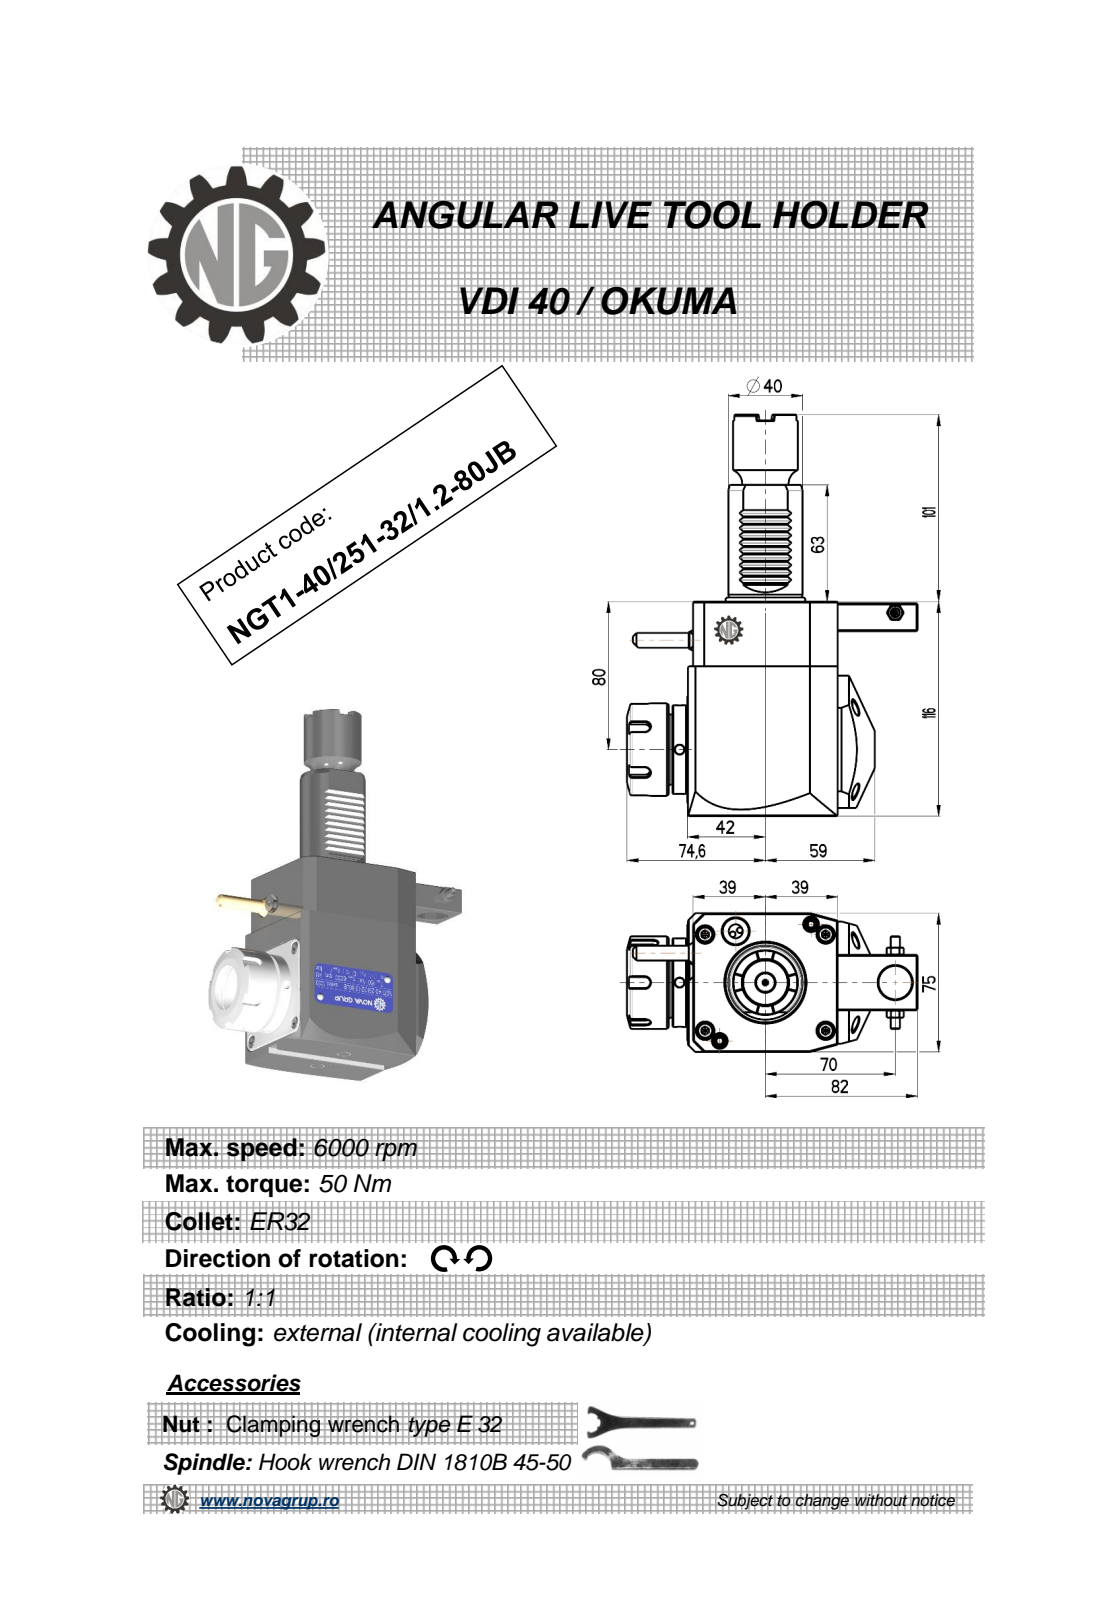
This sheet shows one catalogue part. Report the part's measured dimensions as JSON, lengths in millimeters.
{"part_name": "NGT1_40_251_32_1_2_80JB", "step_written_by": "PRO/ENGINEER BY PARAMETRIC TECHNOLOGY CORPORATION, 2010280 (CONFIG_CONTROL_DESIGN)", "units": "millimeters", "bodies": {"solids": 1, "faces": 466, "planar": 209, "cylindrical": 92, "other": 165}, "overall_size": [217, 156.6, 76.6], "volume_mm3": 914770, "surface_area_mm2": 76313, "round_holes": [[5, 3], [3, 1], [4.2, 1], [9.5, 1], [18, 1], [25, 1], [27, 1]], "round_bosses_or_shafts": [[50, 1], [48, 1], [41, 1], [40, 1], [35, 1], [10, 1], [8.96, 1], [8, 1]], "partial_cylinders_radius": [[0.26, 12], [0.3, 10], [0.2, 6], [3, 5], [0.5, 1], [40, 1]], "face_to_face_distances": [75, 116, 81, 3, 78, 2.8, 80.8, 1, 22.5, 96], "hole_center_spacings": [20.93, 46.25, 61.13, 70, 72.5, 116.25, 137.8]}
